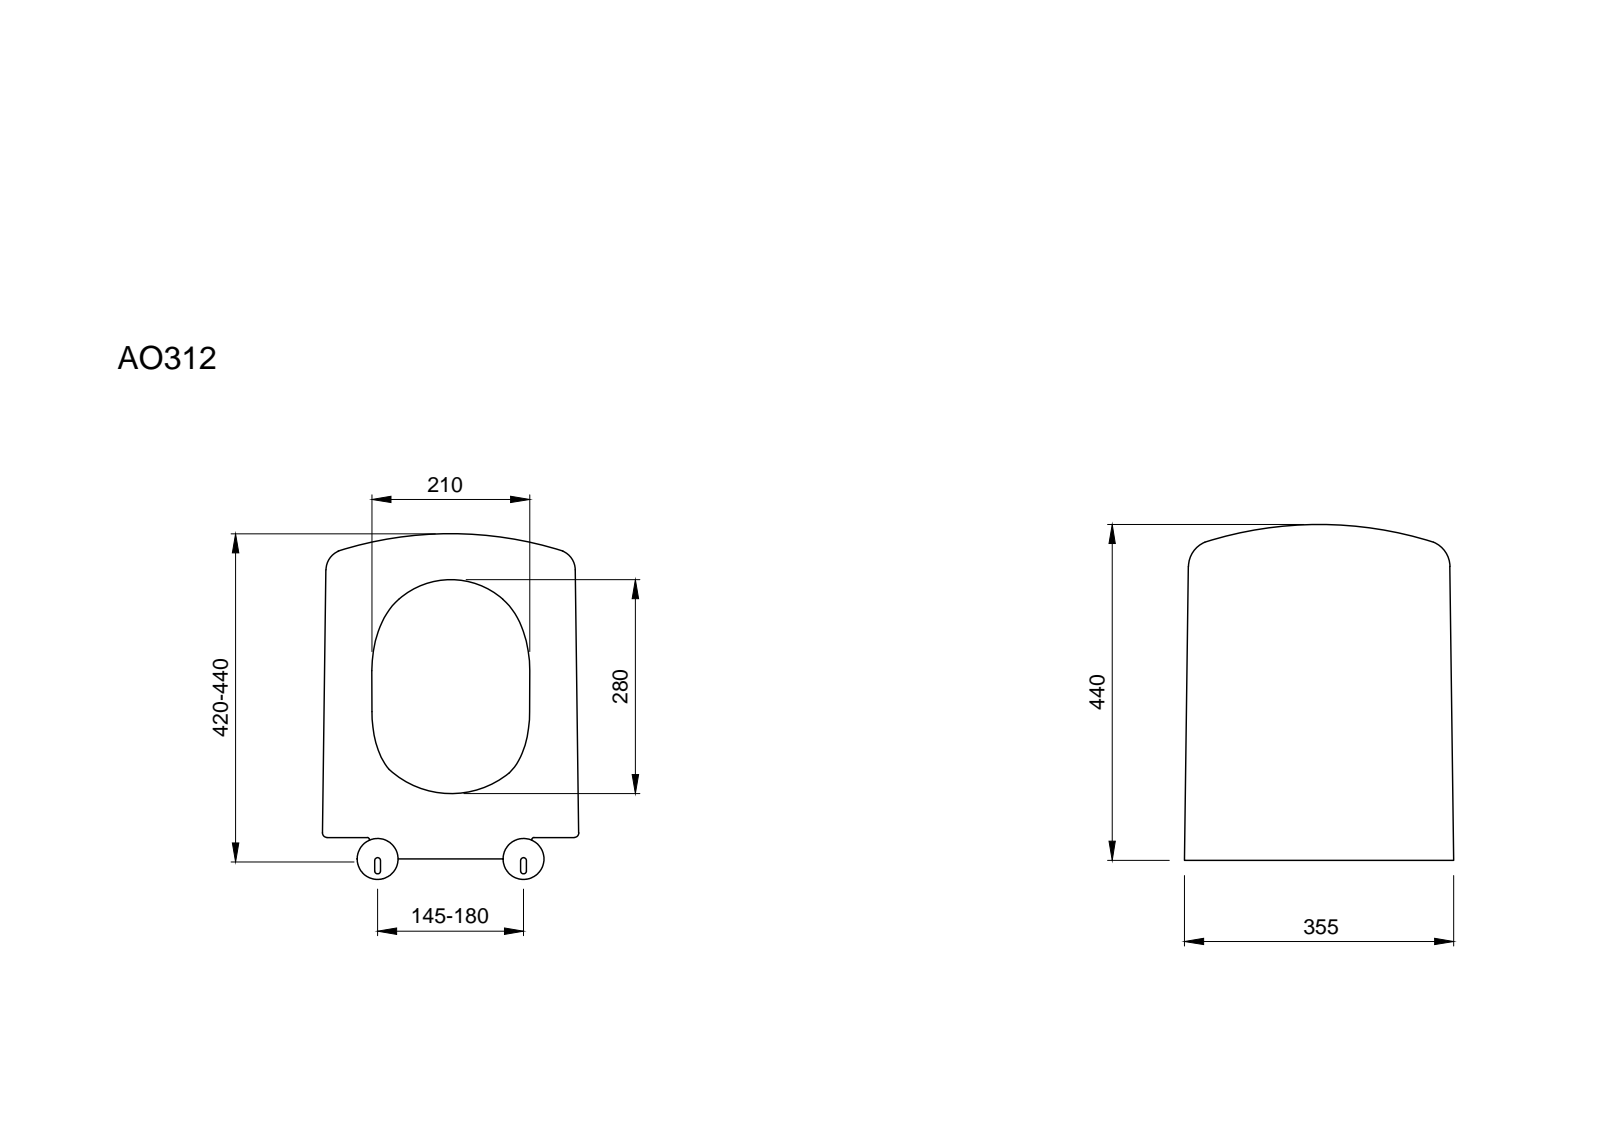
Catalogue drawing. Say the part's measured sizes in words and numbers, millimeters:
Its 3-D file was written by "Rhino 7.21 (CONFIG_CONTROL_DESIGN)". It is 0 solids with 678 faces: 81 planar, 134 cylindrical and 463 other. Overall it measures 500.63 by 449.91 by 356.42 millimeters. Round holes: 8 of diameter 8, 2 of diameter 11.5, 1 of diameter 16, 1 of diameter 17.8. Partial cylindrical surfaces (rounded edges, fillets, slot ends): 24 of radius 1, 16 of radius 1.5, 11 of radius 2, 6 of radius 3, 4 of radius 10, 2 of radius 14.9, 2 of radius 20, 1 of radius 8.9. The main face-to-face distances are 12, 3, 2, 1, 0.75, 233.75, 222.5, 11.25, 221.75, 5.8. The hole center spacings are 20, 174.87, 329.91, 175.6, 176.41, 276.2, 283.36, 313.13.
